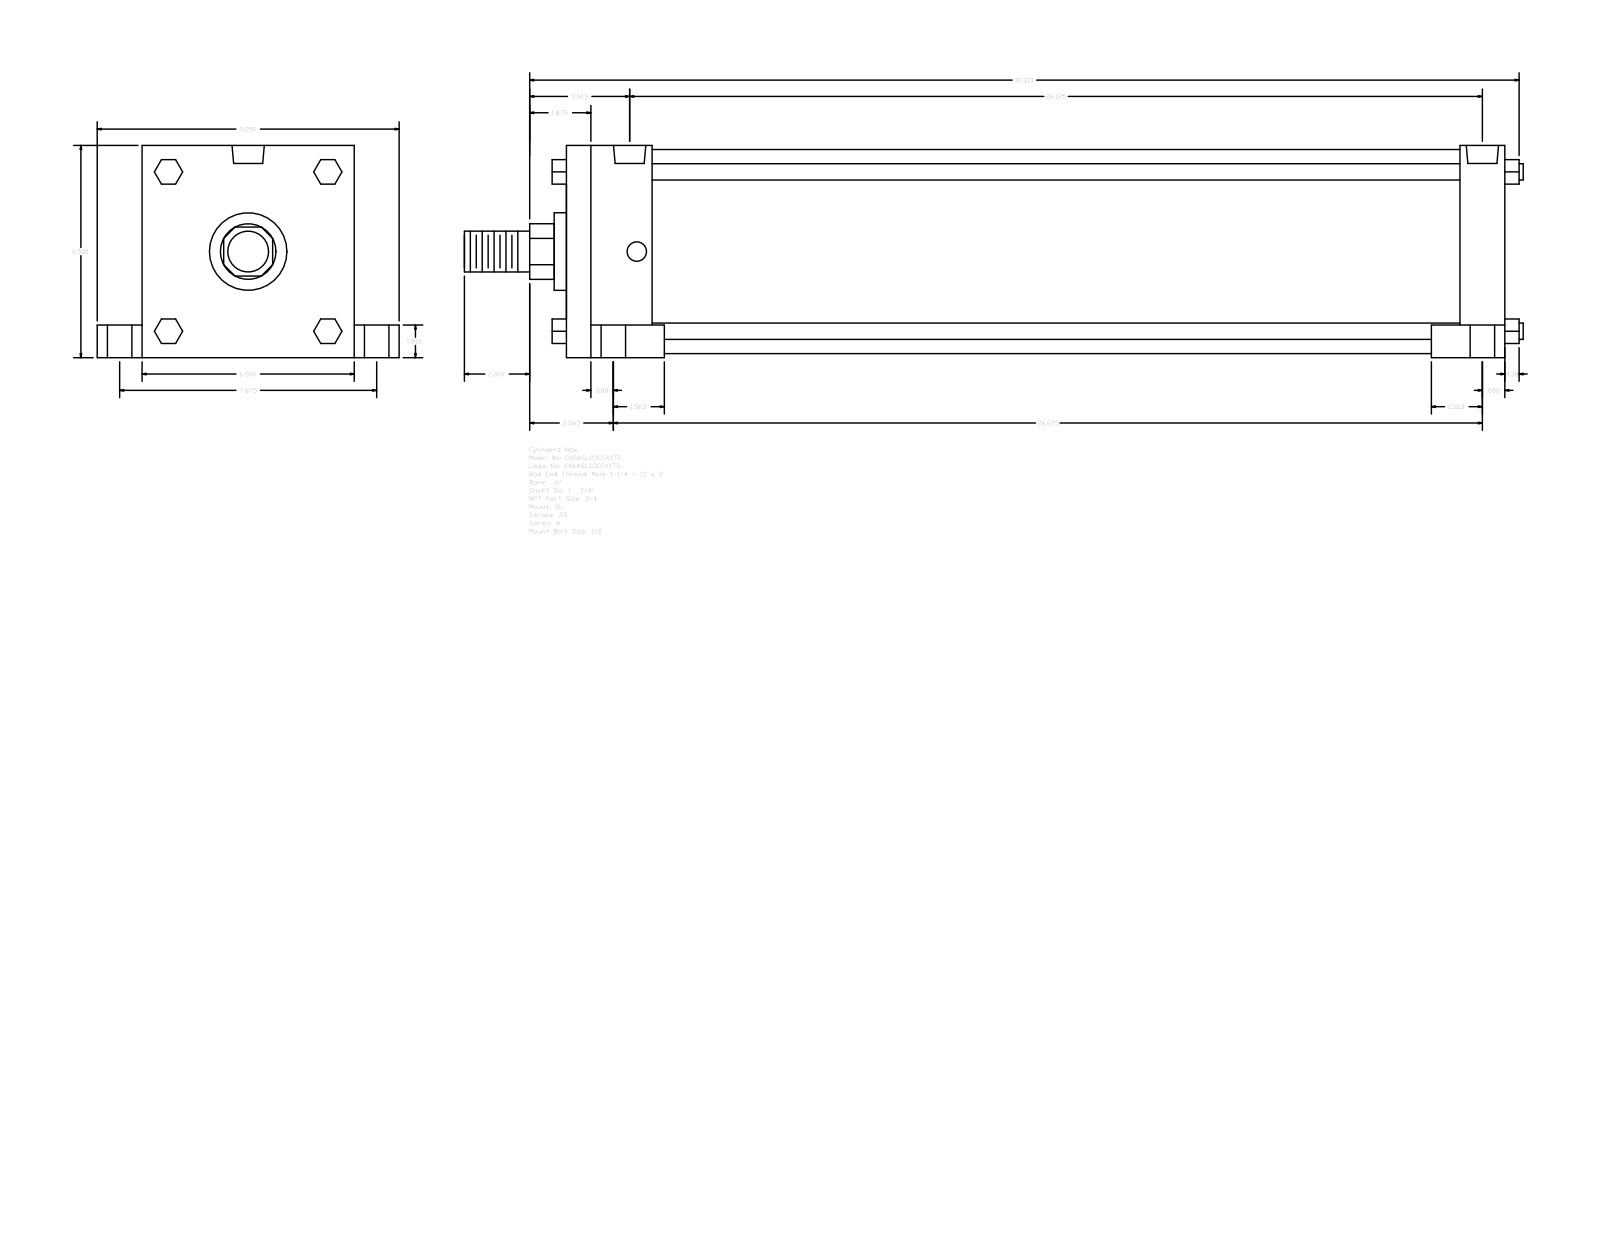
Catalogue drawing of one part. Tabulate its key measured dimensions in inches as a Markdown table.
| quantity | value |
| --- | --- |
| part name | A_SL__0600_1.75 |
| STEP written by | GSSL Pune (CONFIG_CONTROL_DESIGN) |
| units | inches |
| bodies | 0 solids, 150 faces (114 planar, 36 cylindrical, 0 other) |
| overall size | 32.437 × 9.25 × 6.5 |
| round holes (diameter × count) | 0.594 × 4, 0.75 × 4, 1 × 4, 0.989 × 2 |
| round bosses / shafts (diameter × count) | 0.5 × 4, 6.25 × 1, 2.375 × 1, 1.75 × 1, 1.25 × 1 |
| partial cylindrical surfaces (radius × count) | 0.852 × 1 |
| main face-to-face distances | 6.5, 28.75, 2.625, 26.125, 27.375, 24.75, 1.375, 1, 5.5, 1.375 |
| hole center spacings | 0.219, 3.937, 3.943, 3.969, 4.002, 7.875, 25.687, 25.906 |
